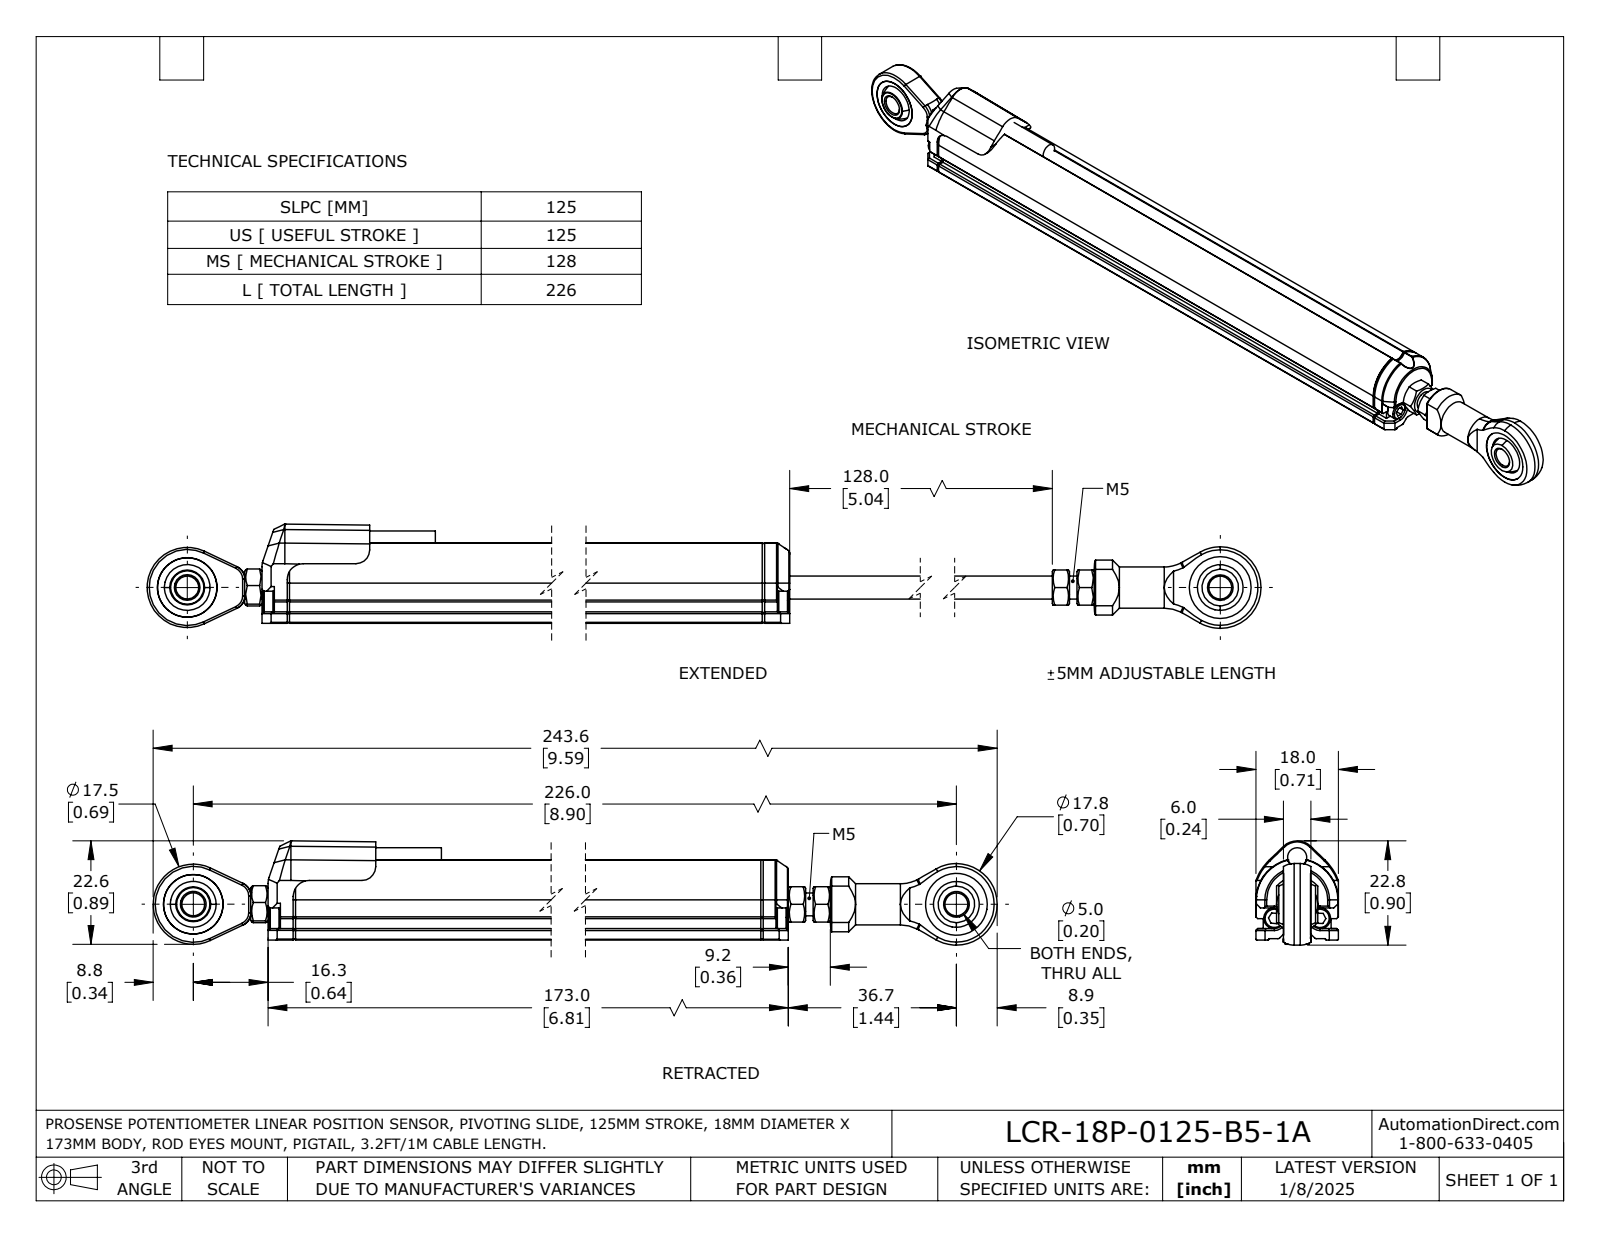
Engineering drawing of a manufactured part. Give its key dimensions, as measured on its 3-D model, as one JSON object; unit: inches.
{"part_name": "LCR-18P-0125-B5-1A", "step_written_by": "SolidWorks 2023 (AUTOMOTIVE_DESIGN)", "units": "inches", "bodies": {"solids": 20, "faces": 515, "planar": 289, "cylindrical": 136, "other": 90}, "overall_size": [9.592, 0.896, 0.709], "volume_in3": 3.16, "surface_area_in2": 36.93, "round_holes": [[0.197, 4], [0.102, 2], [0.104, 2], [0.394, 2], [0.213, 1], [0.272, 1], [0.512, 1], [0.531, 1]], "round_bosses_or_shafts": [[0.181, 4], [0.113, 3], [0.059, 2], [0.354, 1], [0.165, 1], [0.113, 1]], "partial_cylinders_radius": [[0.008, 12], [0.004, 10], [0.02, 8], [0.012, 6], [0.018, 6], [0.016, 4], [0.039, 4], [0.043, 4]], "face_to_face_distances": [0.709, 0.02, 6.358, 0.236, 0.059, 0.071, 0.063, 0.646, 6.339, 0.087], "hole_center_spacings": [0.231, 0.394, 0.23, 0.231, 8.898]}
